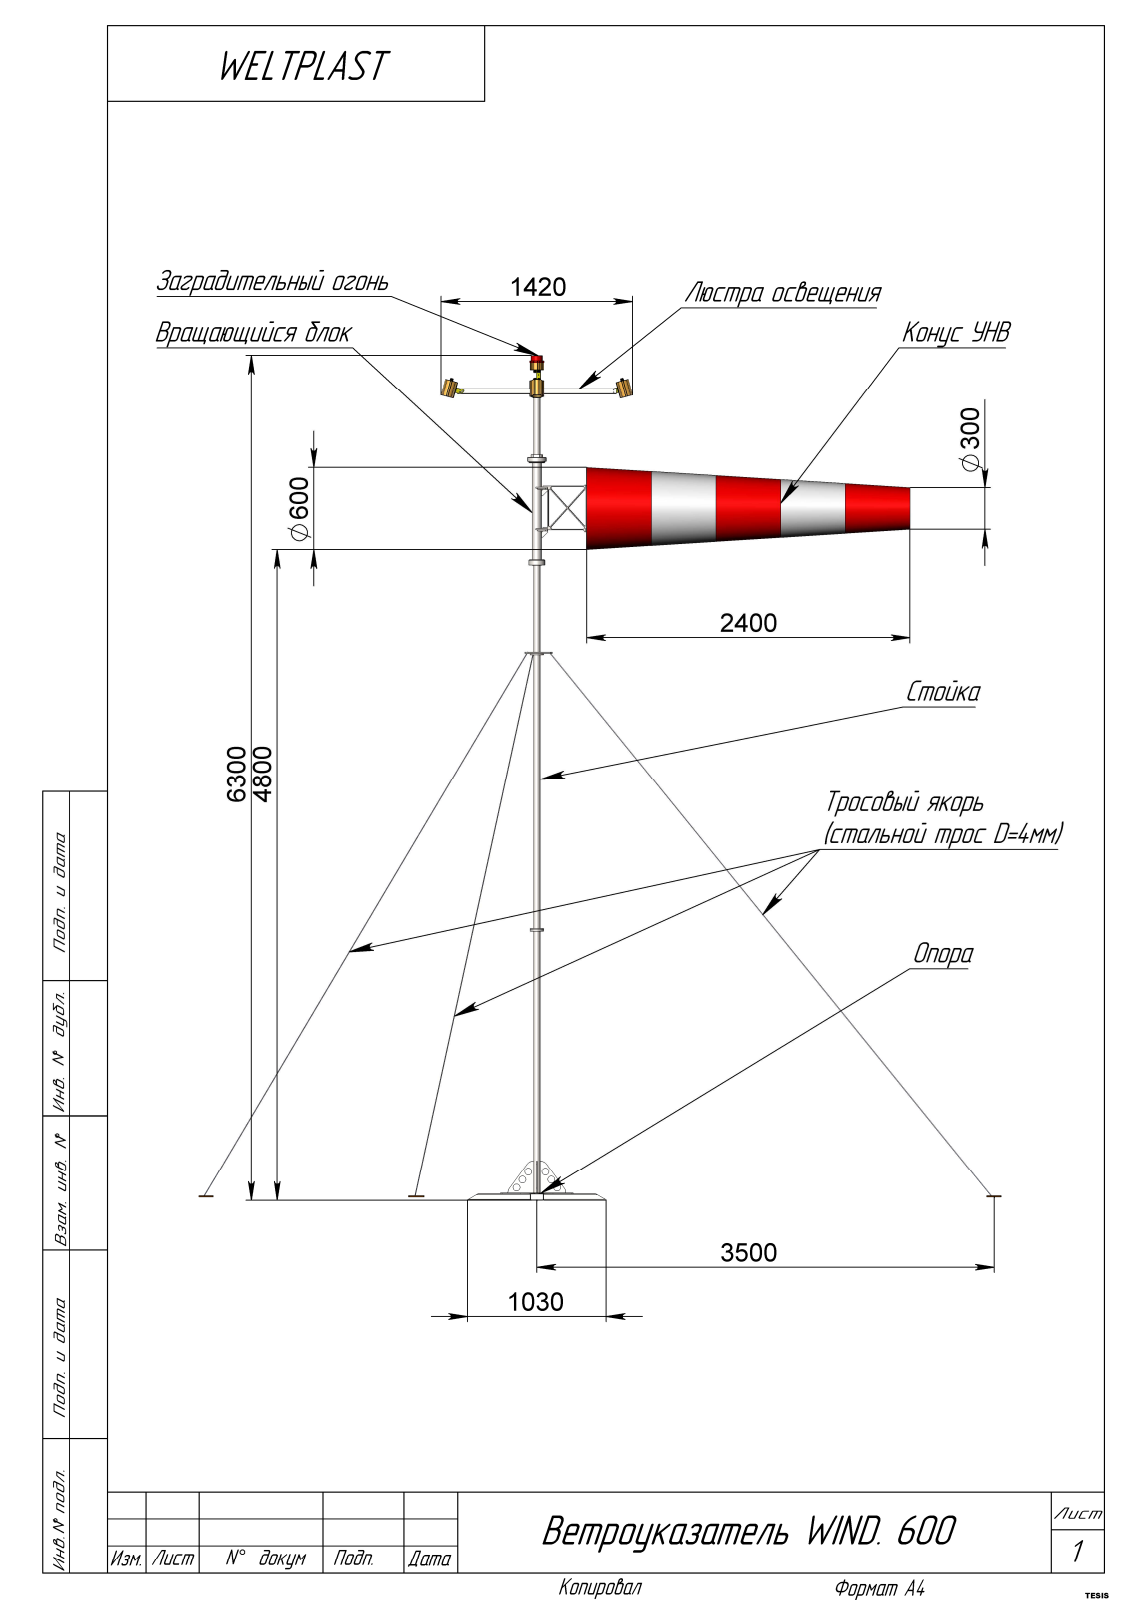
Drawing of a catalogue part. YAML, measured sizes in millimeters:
part_name: "подшипник 1212 сферический макет.; Нижняя Крышка; WIND.022 (кольцо 600мм); WIND.011 (труба внешняя) (+8 more)"
step_written_by: "SolidWorks 2017 (AUTOMOTIVE_DESIGN)"
units: millimeters
bodies: {solids: 91, faces: 2435, planar: 710, cylindrical: 1537, other: 188}
overall_size: [6267.99, 5977.48, 5956.33]
volume: 11750000
surface_area: 12690000
round_holes:
  - {diameter: 4.4, count: 54}
  - {diameter: 6, count: 30}
  - {diameter: 52, count: 12}
  - {diameter: 12.6, count: 10}
  - {diameter: 20.25, count: 10}
  - {diameter: 12, count: 9}
  - {diameter: 14, count: 8}
  - {diameter: 4.5, count: 6}
  - {diameter: 5, count: 6}
  - {diameter: 11, count: 6}
  - {diameter: 79, count: 5}
  - {diameter: 8, count: 4}
round_bosses_or_shafts:
  - {diameter: 8, count: 12}
  - {diameter: 21.5, count: 10}
  - {diameter: 19.7, count: 10}
  - {diameter: 4, count: 3}
  - {diameter: 140, count: 1}
  - {diameter: 120, count: 1}
  - {diameter: 100, count: 1}
  - {diameter: 95, count: 1}
partial_cylinders:
  - {radius: 5, count: 145}
  - {radius: 4, count: 62}
  - {radius: 10, count: 22}
  - {radius: 2, count: 20}
  - {radius: 4.5, count: 18}
  - {radius: 1.5, count: 14}
  - {radius: 2.5, count: 12}
  - {radius: 3, count: 10}
face_to_face_distances: [4, 46, 42, 2, 6, 56, 38, 11, 13, 7]
hole_center_spacings: [47.5, 82.27, 95, 33.5, 61.5, 82.28, 28, 47.52]
